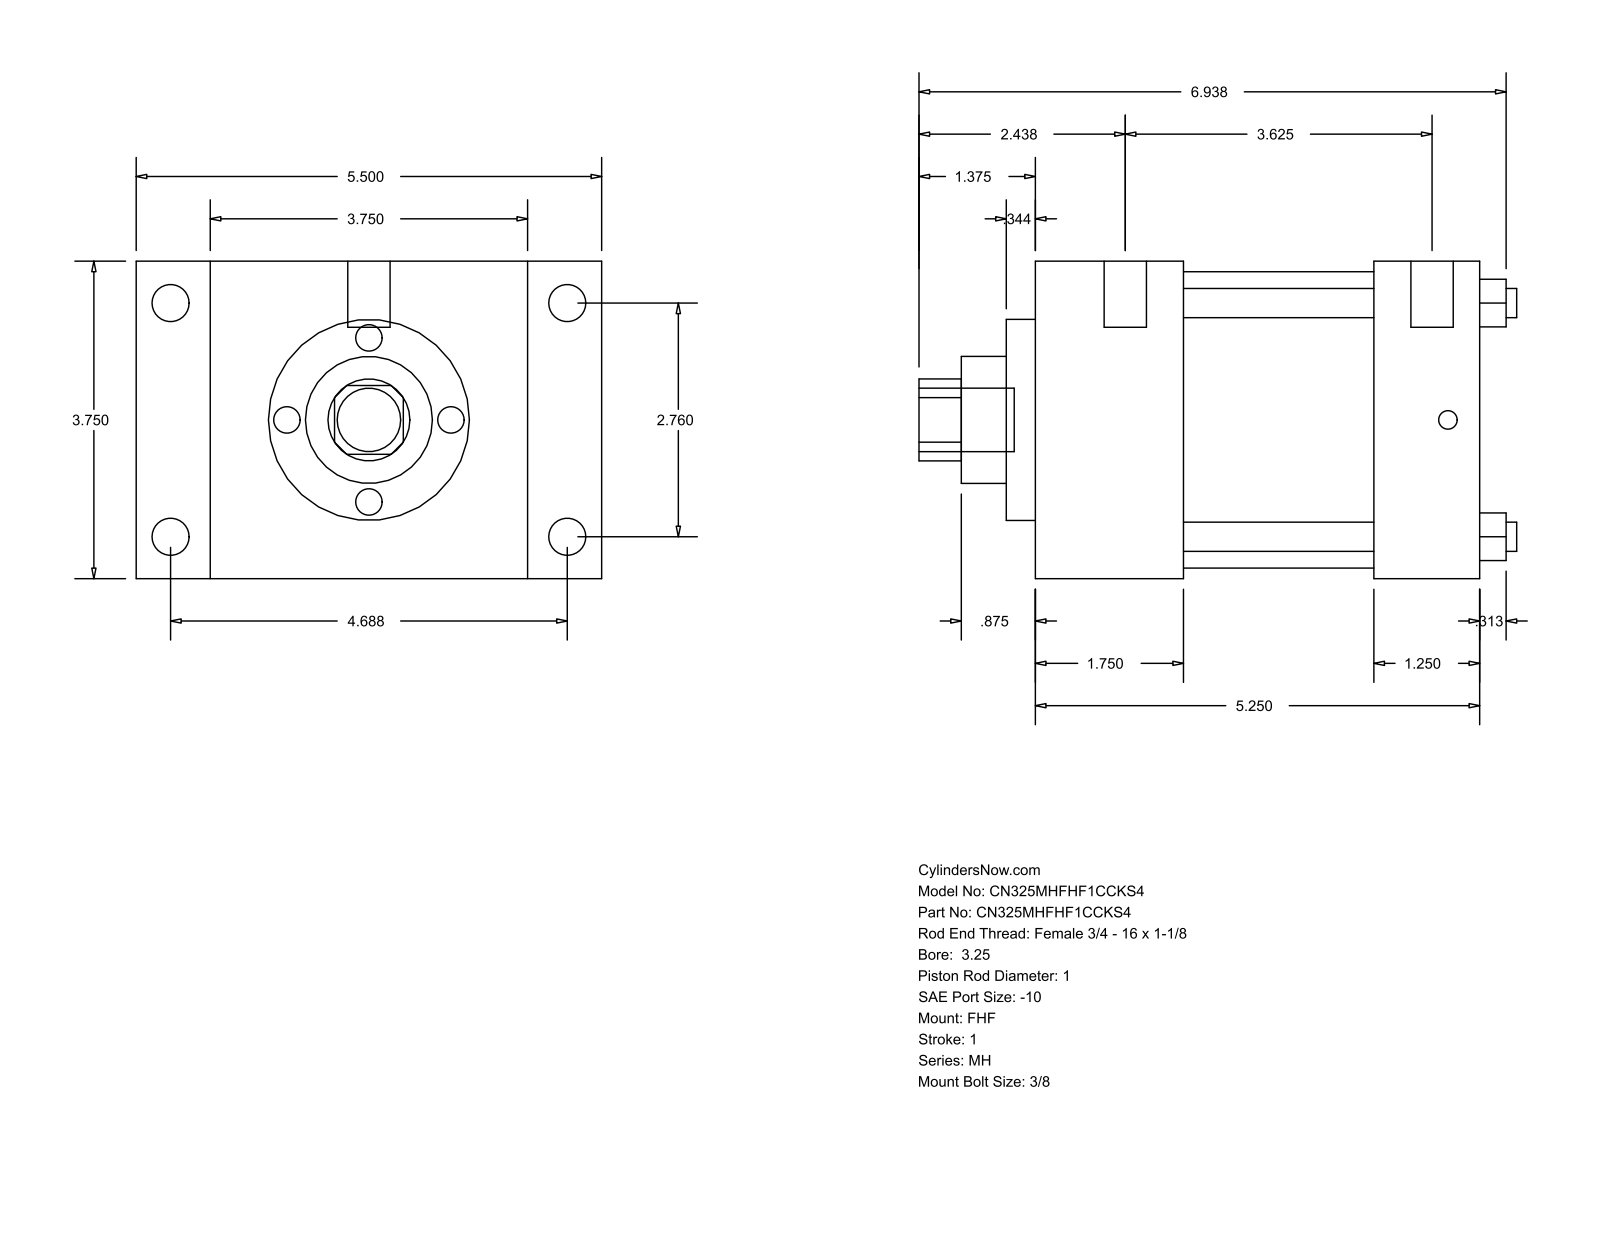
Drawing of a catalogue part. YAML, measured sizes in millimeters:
part_name: "MH_FHF__0325_1"
step_written_by: "GSSL Pune (CONFIG_CONTROL_DESIGN)"
units: millimeters
bodies: {solids: 0, faces: 90, planar: 61, cylindrical: 29, other: 0}
overall_size: [179.39, 139.7, 95.25]
round_holes:
  - {diameter: 8.76, count: 4}
  - {diameter: 25.4, count: 1}
  - {diameter: 38.1, count: 1}
  - {diameter: 60.33, count: 1}
  - {diameter: 88.9, count: 1}
round_bosses_or_shafts:
  - {diameter: 11.13, count: 4}
  - {diameter: 5.56, count: 4}
  - {diameter: 12.7, count: 2}
  - {diameter: 19.05, count: 1}
partial_cylinders:
  - {radius: 12.29, count: 1}
face_to_face_distances: [95.24, 133.36, 44.46, 88.9, 22.23, 117.47, 139.7, 101.61, 57.15, 31.75]
hole_center_spacings: [49.57, 70.1, 99.14]
